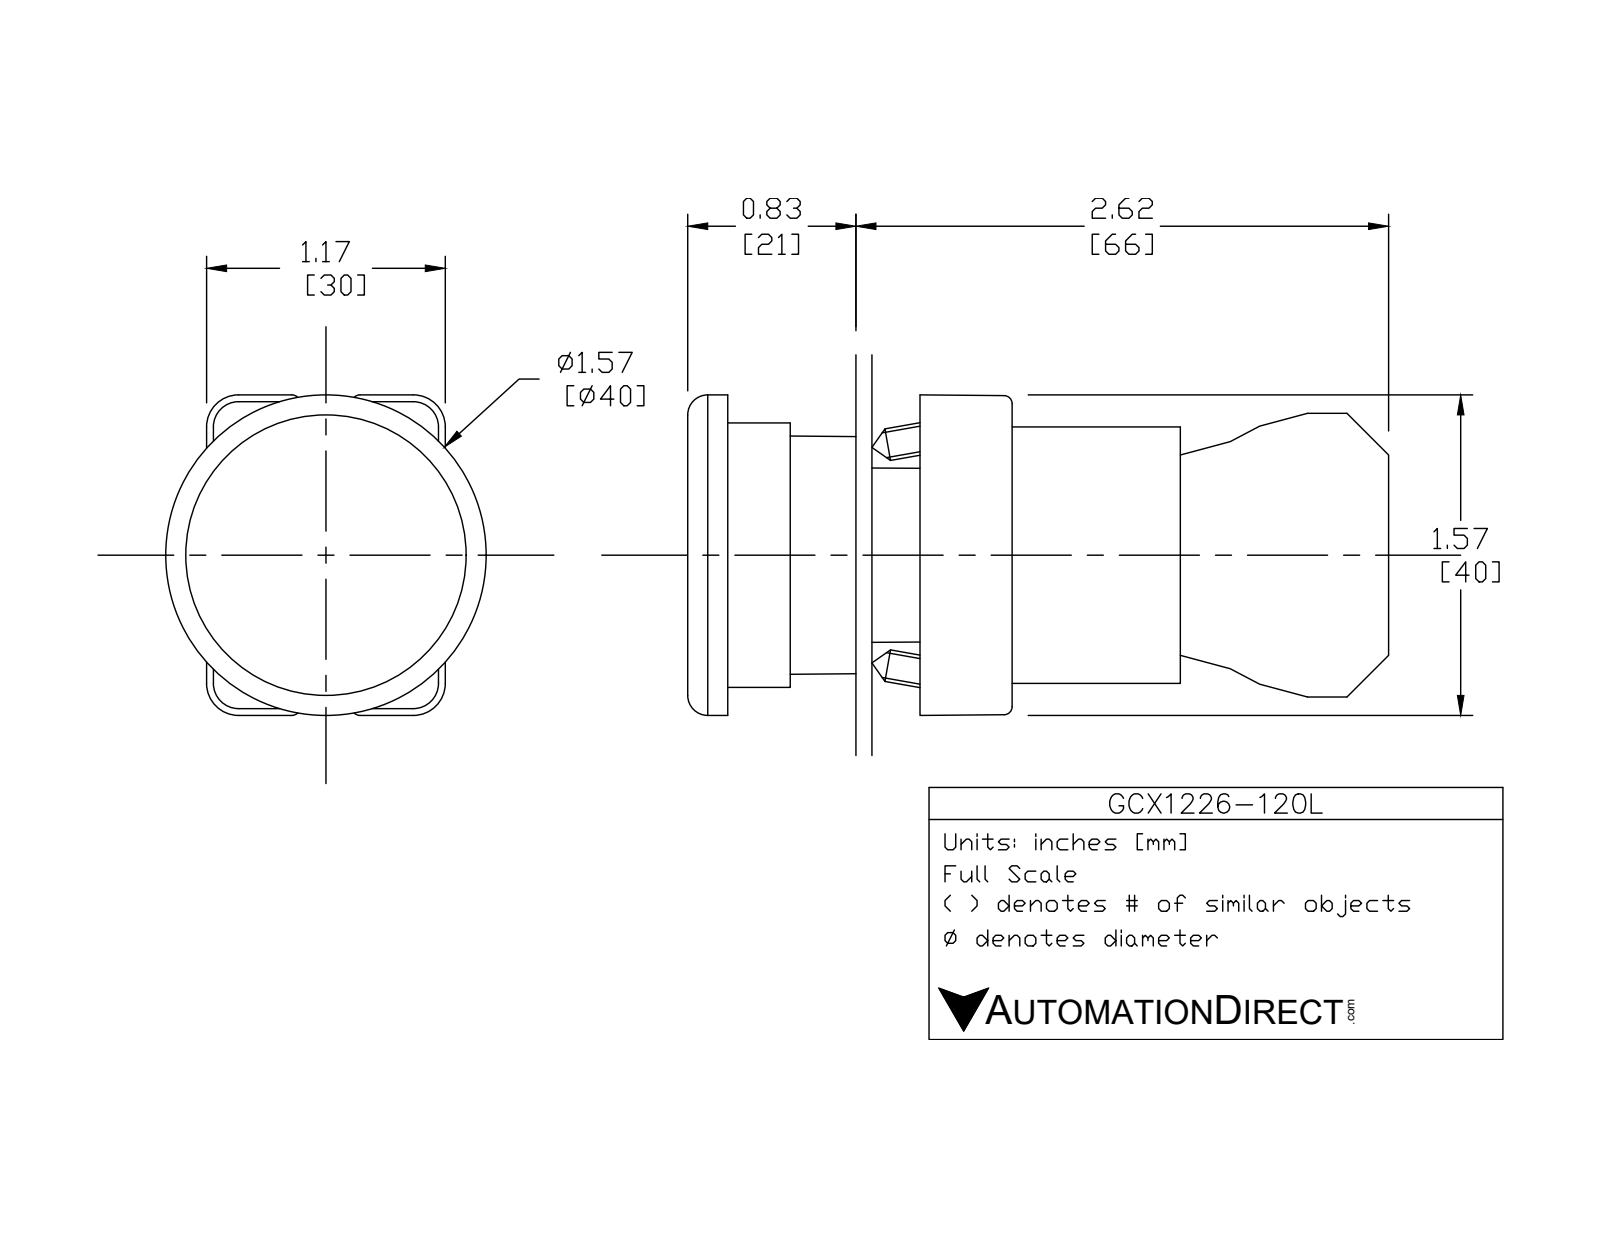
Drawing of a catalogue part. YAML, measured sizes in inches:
part_name: "ECX1050; GCX1226-120L; ecx1030; GCX122X OPERATOR (+1 more)"
step_written_by: "SolidWorks 2016 (AUTOMOTIVE_DESIGN)"
units: inches
bodies: {solids: 7, faces: 431, planar: 252, cylindrical: 146, other: 33}
overall_size: [3.469, 1.581, 1.575]
volume: 2.895
surface_area: 40.89
round_holes:
  - {diameter: 0.079, count: 2}
  - {diameter: 0.124, count: 2}
  - {diameter: 0.13, count: 2}
  - {diameter: 0.087, count: 1}
  - {diameter: 0.197, count: 1}
  - {diameter: 0.469, count: 1}
  - {diameter: 0.878, count: 1}
  - {diameter: 0.888, count: 1}
  - {diameter: 1.024, count: 1}
  - {diameter: 1.181, count: 1}
round_bosses_or_shafts:
  - {diameter: 0.157, count: 4}
  - {diameter: 1.299, count: 1}
  - {diameter: 1.175, count: 1}
  - {diameter: 0.945, count: 1}
  - {diameter: 0.856, count: 1}
  - {diameter: 0.78, count: 1}
  - {diameter: 0.504, count: 1}
partial_cylinders:
  - {radius: 0.059, count: 24}
  - {radius: 0.041, count: 12}
  - {radius: 0.124, count: 12}
  - {radius: 0.157, count: 12}
  - {radius: 0.039, count: 8}
  - {radius: 0.128, count: 2}
  - {radius: 0.02, count: 1}
  - {radius: 0.063, count: 1}
face_to_face_distances: [0.827, 2.445, 1.618, 0.579, 2.287, 1.461, 0.157, 0.587, 0.031, 1.165]
hole_center_spacings: [0.236, 0.539, 0.472, 0.484]
